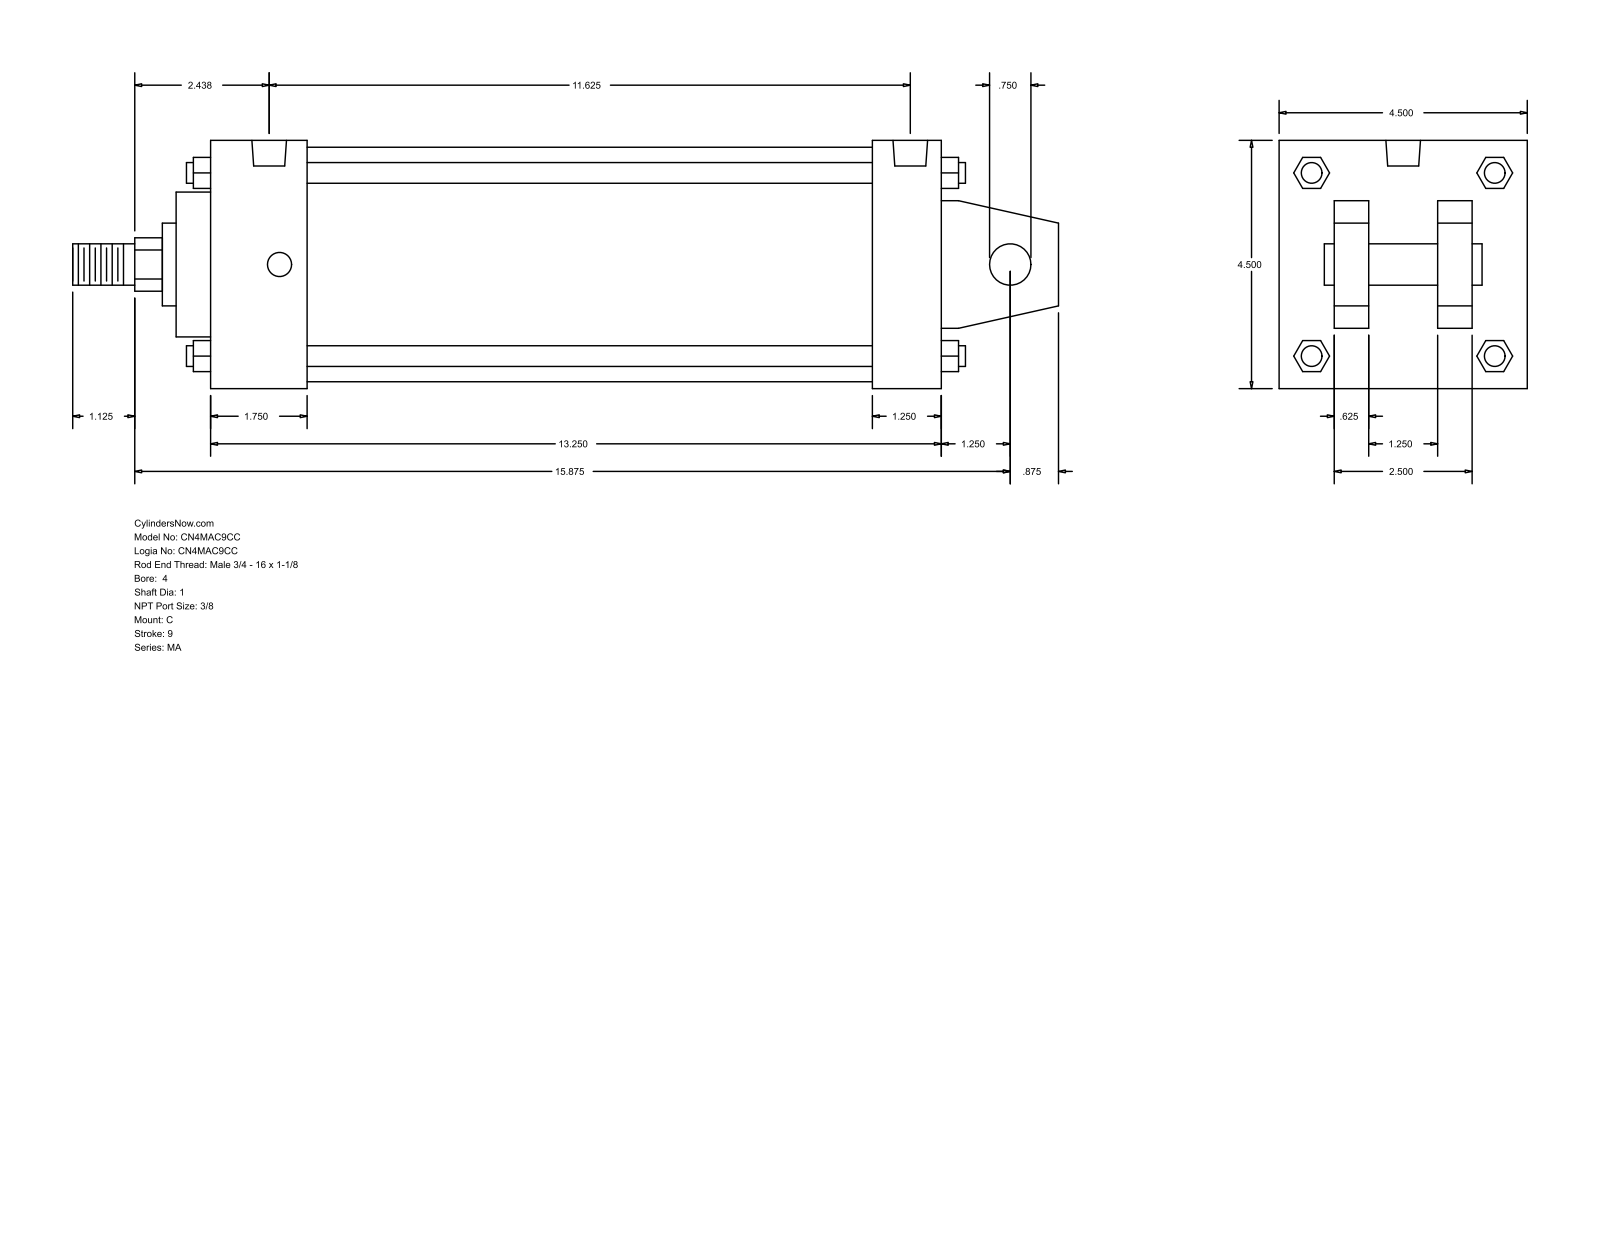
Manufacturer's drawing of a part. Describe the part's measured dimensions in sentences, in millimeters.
The part is named "MA_C__0400_1". Its 3-D file was written by "GSSL Pune (CONFIG_CONTROL_DESIGN)". It is 0 solids with 141 faces: 109 planar, 32 cylindrical and 0 other. Overall it measures 454.02 by 114.3 by 114.3 millimeters. Round holes: 4 of diameter 11.11, 2 of diameter 15.93. Round bosses or shafts: 4 of diameter 9.53, 2 of diameter 19.05, 1 of diameter 107.95, 1 of diameter 66.67, 1 of diameter 38.1, 1 of diameter 25.4. Partial cylindrical surfaces (rounded edges, fillets, slot ends): 1 of radius 12.29. The main face-to-face distances are 114.3, 336.56, 15.87, 73.03, 41.27, 25.4, 88.9, 47.63, 304.81, 31.75. The hole center spacings are 4.76, 285.76, 290.52, 295.28.
